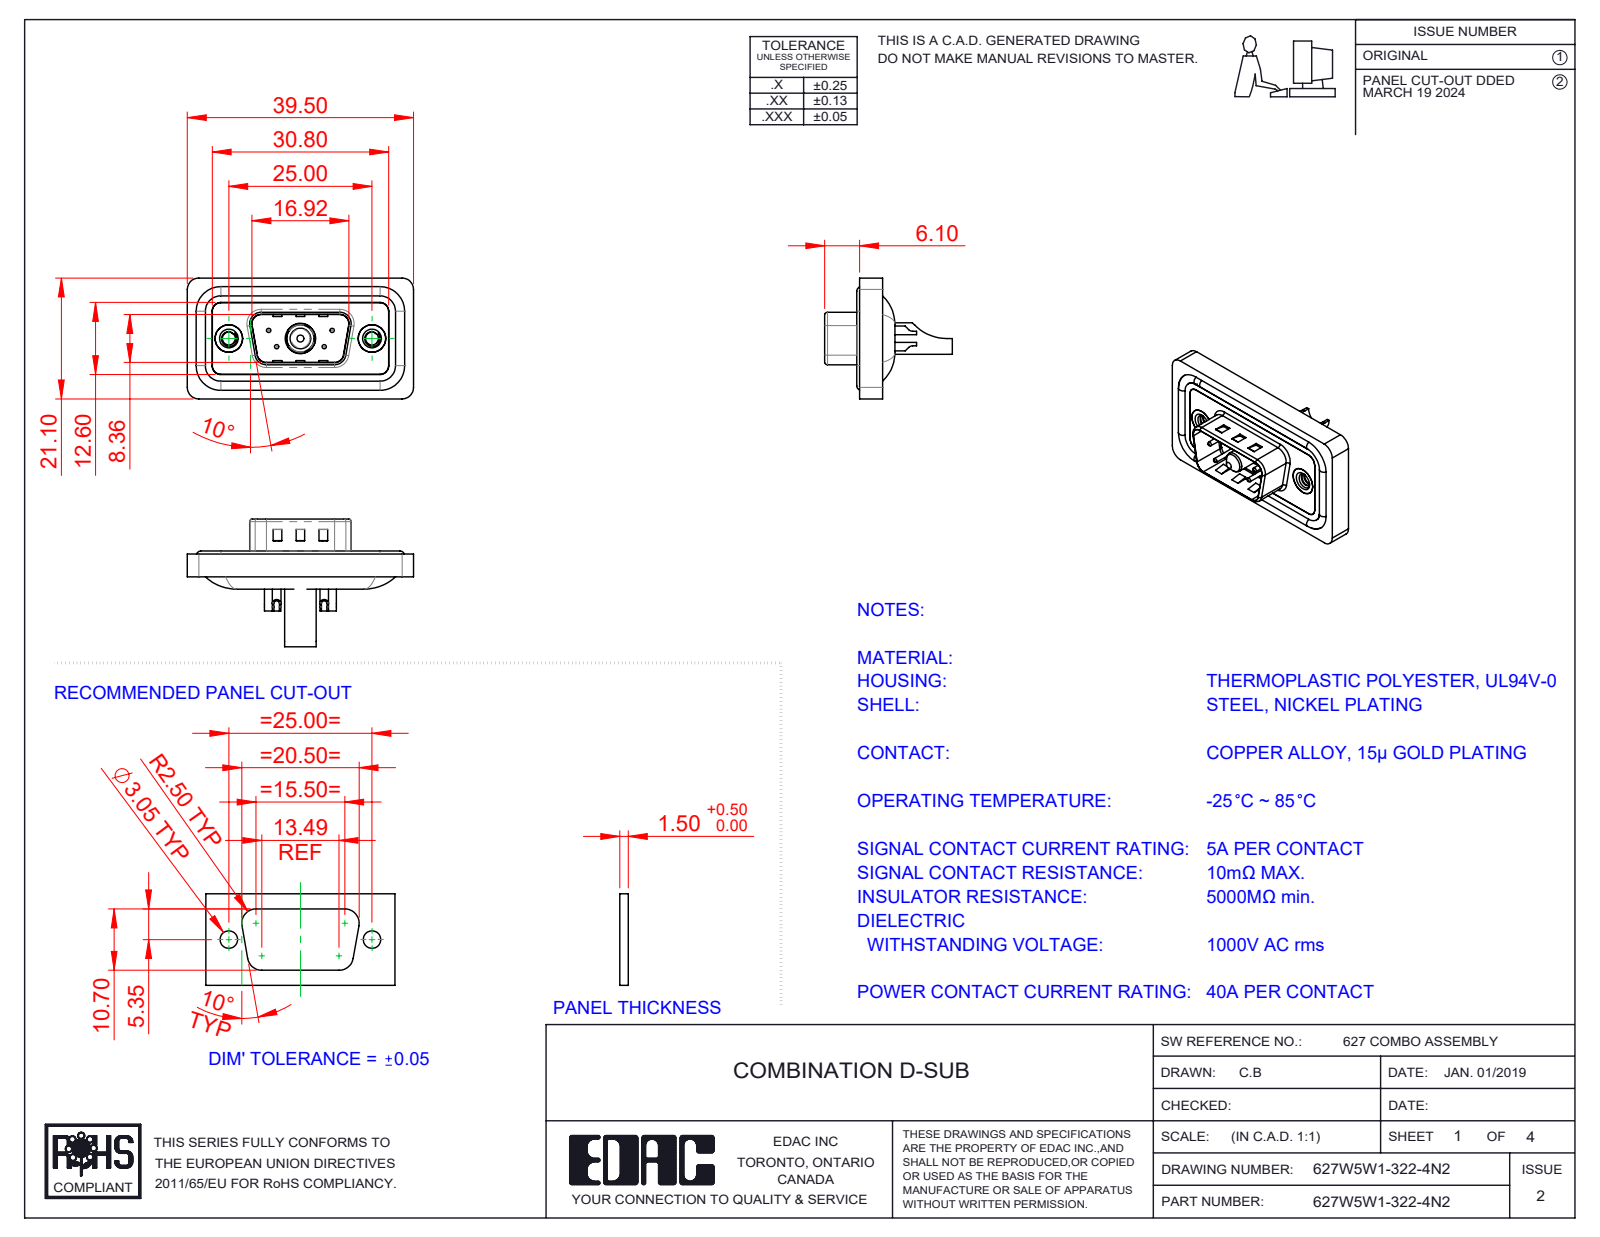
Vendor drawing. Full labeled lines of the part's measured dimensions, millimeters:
Part name (STEP PRODUCT): 627W5W1-322-4N2; 627Combo Shell Front_09 Contacts; 627Combo Waterproof Housing_09 Contacts; 627Combo Contact Row 1_22 (+5 more)
STEP written by: SolidWorks 2023 (CONFIG_CONTROL_DESIGN)
Units: millimetres
Bodies: 13 solids, 602 faces (193 planar, 264 cylindrical, 145 other)
Overall size (bounding box): 39.5 × 22.3 × 21.1
Volume: 4 434 mm³ · Surface area: 7 113 mm²
Round holes (diameter × count): ⌀0.75 ×4, ⌀1 ×4, ⌀1.6 ×4, ⌀2 ×4, ⌀2.26 ×2, ⌀4 ×2, ⌀4.8 ×2, ⌀5 ×2, ⌀4.6 ×1, ⌀4.85 ×1, ⌀5.3 ×1
Round bosses / shafts (diameter × count): ⌀1.6 ×4, ⌀1.5 ×4, ⌀4.9 ×2, ⌀5.5 ×1, ⌀5.2 ×1, ⌀4.75 ×1, ⌀3.75 ×1, ⌀3.6 ×1
Partial cylindrical surfaces — rounded edges, fillets, slot ends (radius × count): R1.5 ×22, R2 ×18, R0.5 ×8, R1.6 ×8, R1 ×6, R0.25 ×4, R0.6 ×4, R0.65 ×4
Main face-to-face distances: 0.4, 1.1, 2.9, 1.6, 3.1, 0.5, 1.5, 2.5, 4, 0.8
Hole centre spacings: 3.16, 5.72, 7.1, 12.5, 18.1, 4.39, 4.4, 8.31
